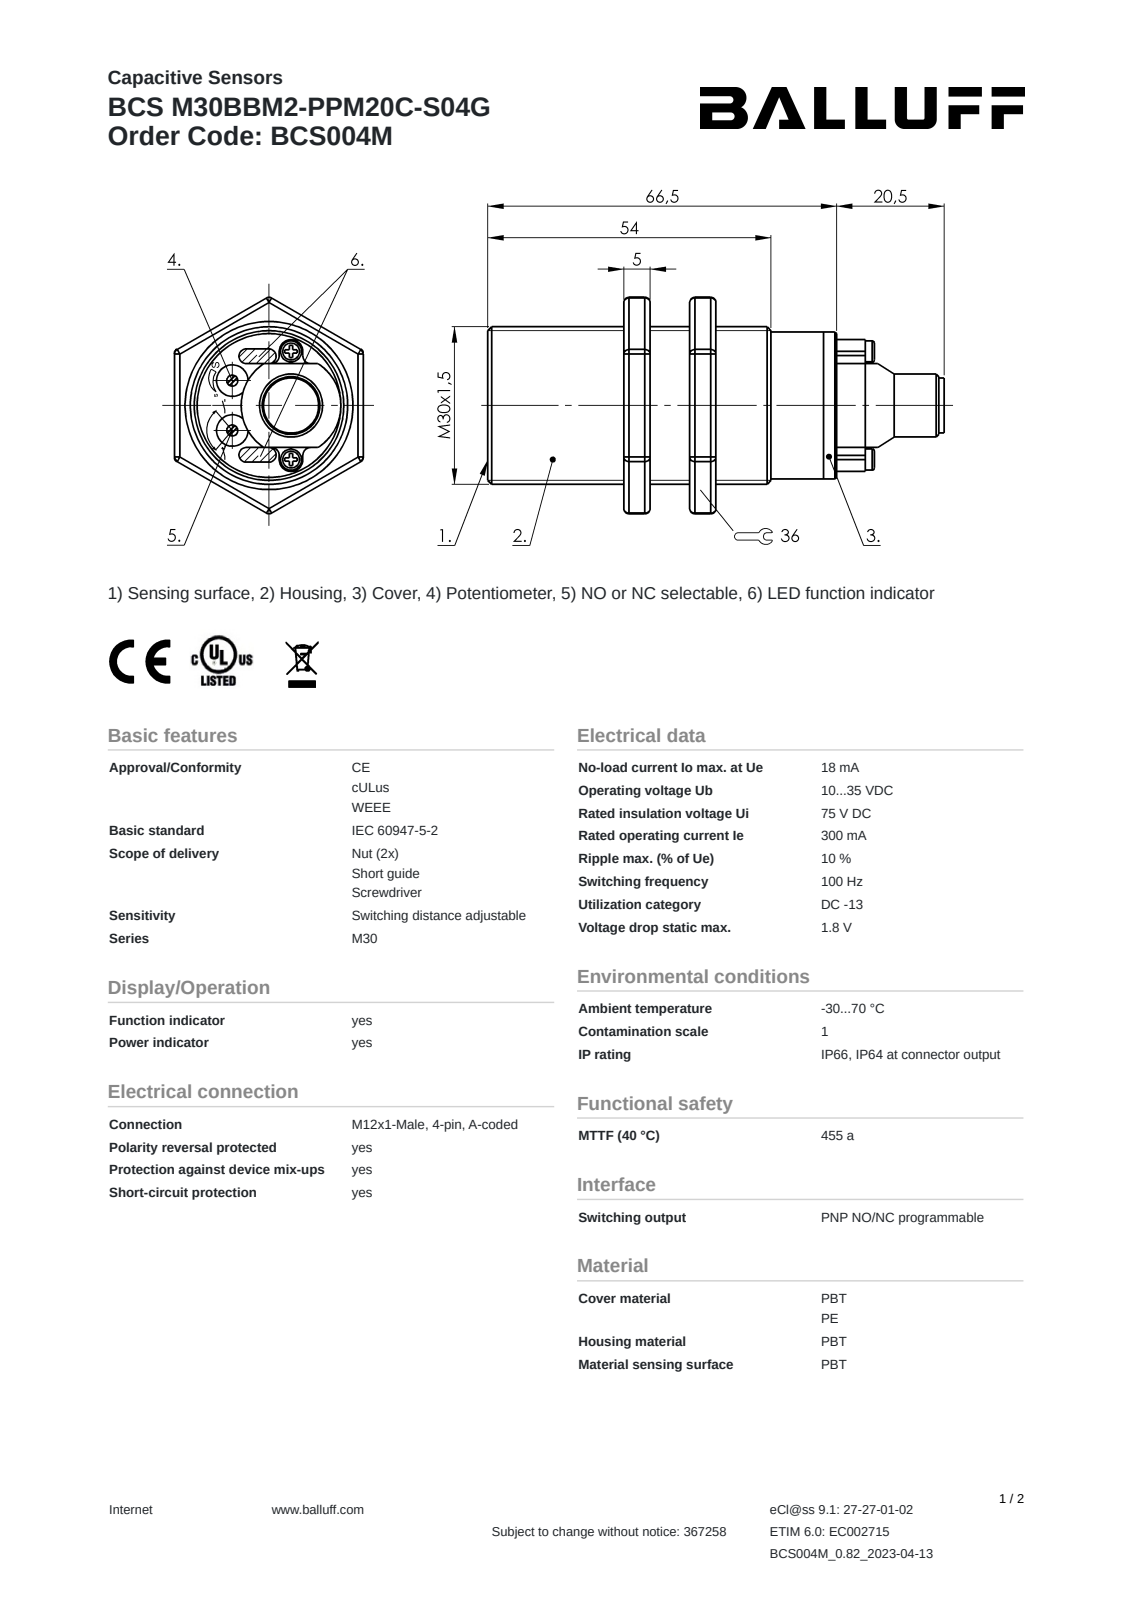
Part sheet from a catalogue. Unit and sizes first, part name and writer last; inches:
Units: inches
Overall size (bounding box): 3.425 × 1.637 × 1.417
Round holes (diameter × count): ⌀0.098 ×2, ⌀0.197 ×2, ⌀0.327 ×1, ⌀1.117 ×1
Round bosses / shafts (diameter × count): ⌀0.039 ×4, ⌀0.157 ×2, ⌀1.181 ×1, ⌀1.102 ×1, ⌀1.094 ×1, ⌀0.472 ×1, ⌀0.409 ×1
Partial cylindrical surfaces — rounded edges, fillets, slot ends (radius × count): R0.05 ×4, R0.059 ×4, R0.089 ×2, R0.024 ×1, R0.368 ×1, R0.374 ×1
Main face-to-face distances: 0.315, 0.197, 1.417, 0.965, 1.161, 1.28, 0.512, 1.476, 0.118, 1.142
Hole centre spacings: 0.333, 0.479, 0.165, 0.374
Volume: 3.278 in³ · Surface area: 19.5 in²
Bodies: 3 solids, 156 faces (85 planar, 32 cylindrical, 39 other)
Part name (STEP PRODUCT): BCS004M
STEP written by: SolidWorks 2021 (AUTOMOTIVE_DESIGN)
